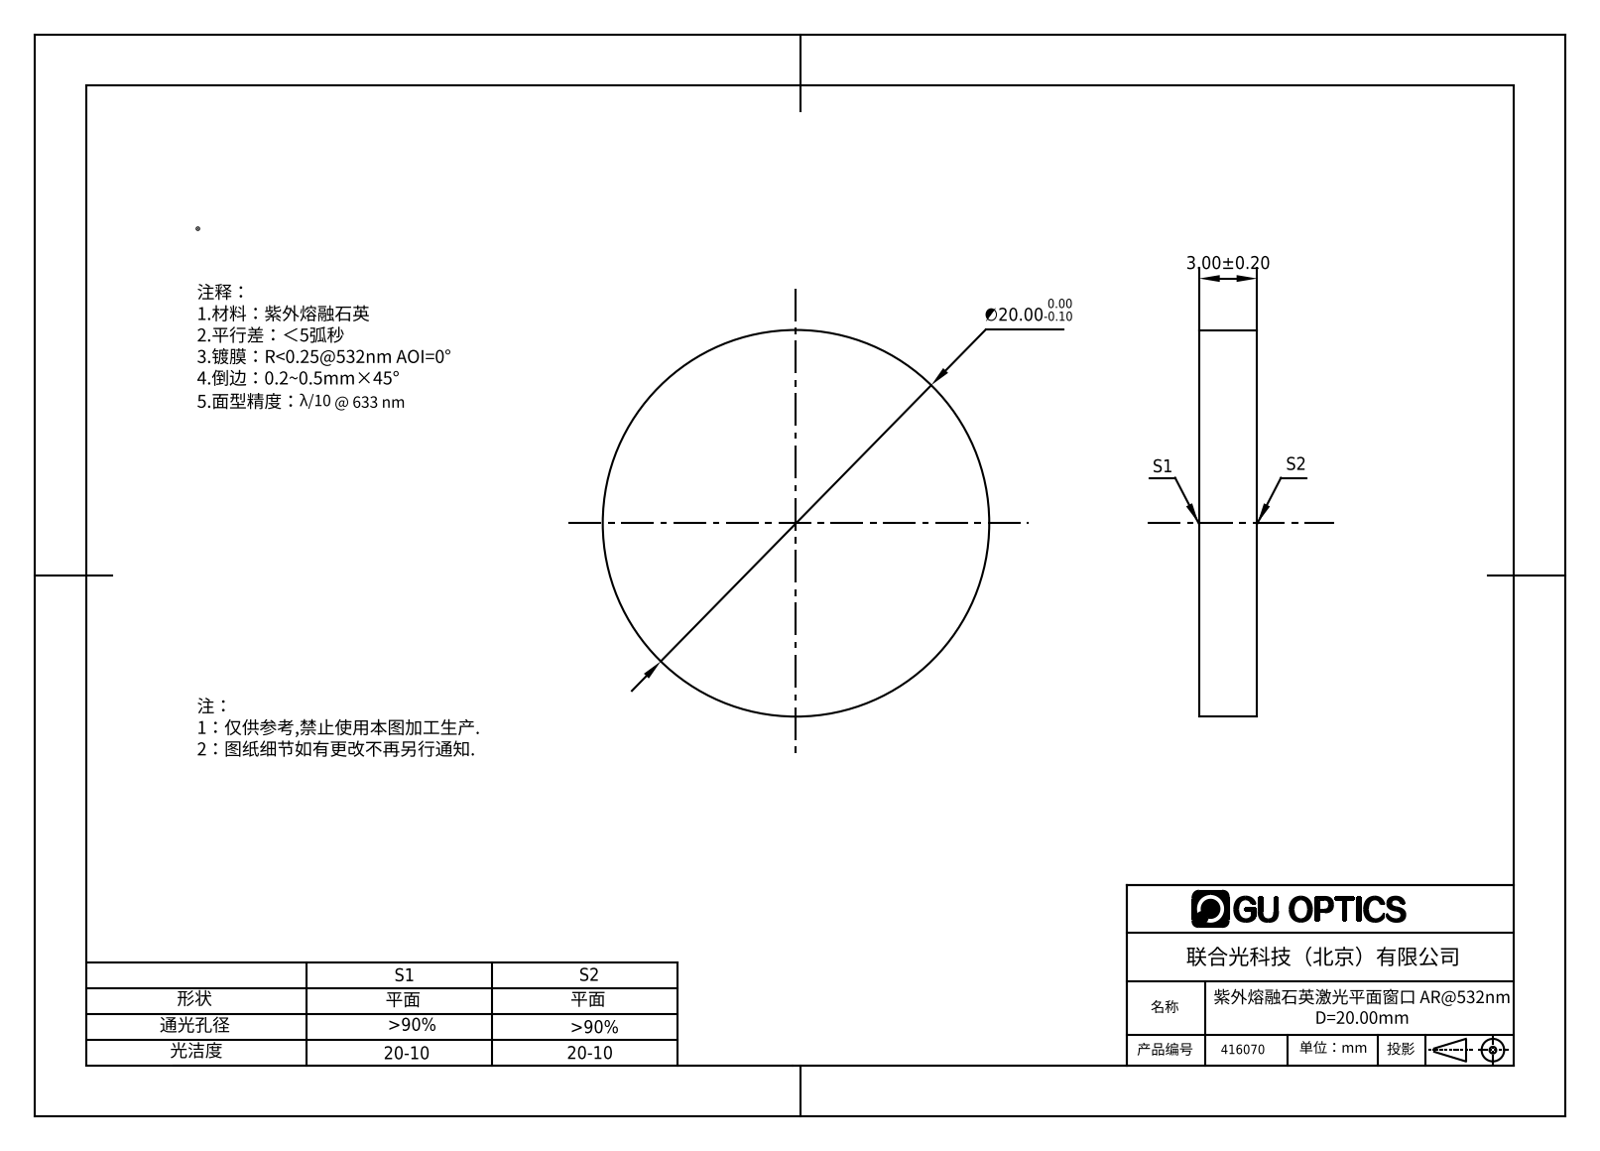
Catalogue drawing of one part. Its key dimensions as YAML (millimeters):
part_name: "416048"
step_written_by: "SolidWorks 2016 (CONFIG_CONTROL_DESIGN)"
units: millimeters
bodies: {solids: 1, faces: 4, planar: 2, cylindrical: 2, other: 0}
overall_size: [20, 20, 3]
volume: 942
surface_area: 817
round_bosses_or_shafts:
  - {diameter: 20, count: 1}
face_to_face_distances: [3]
